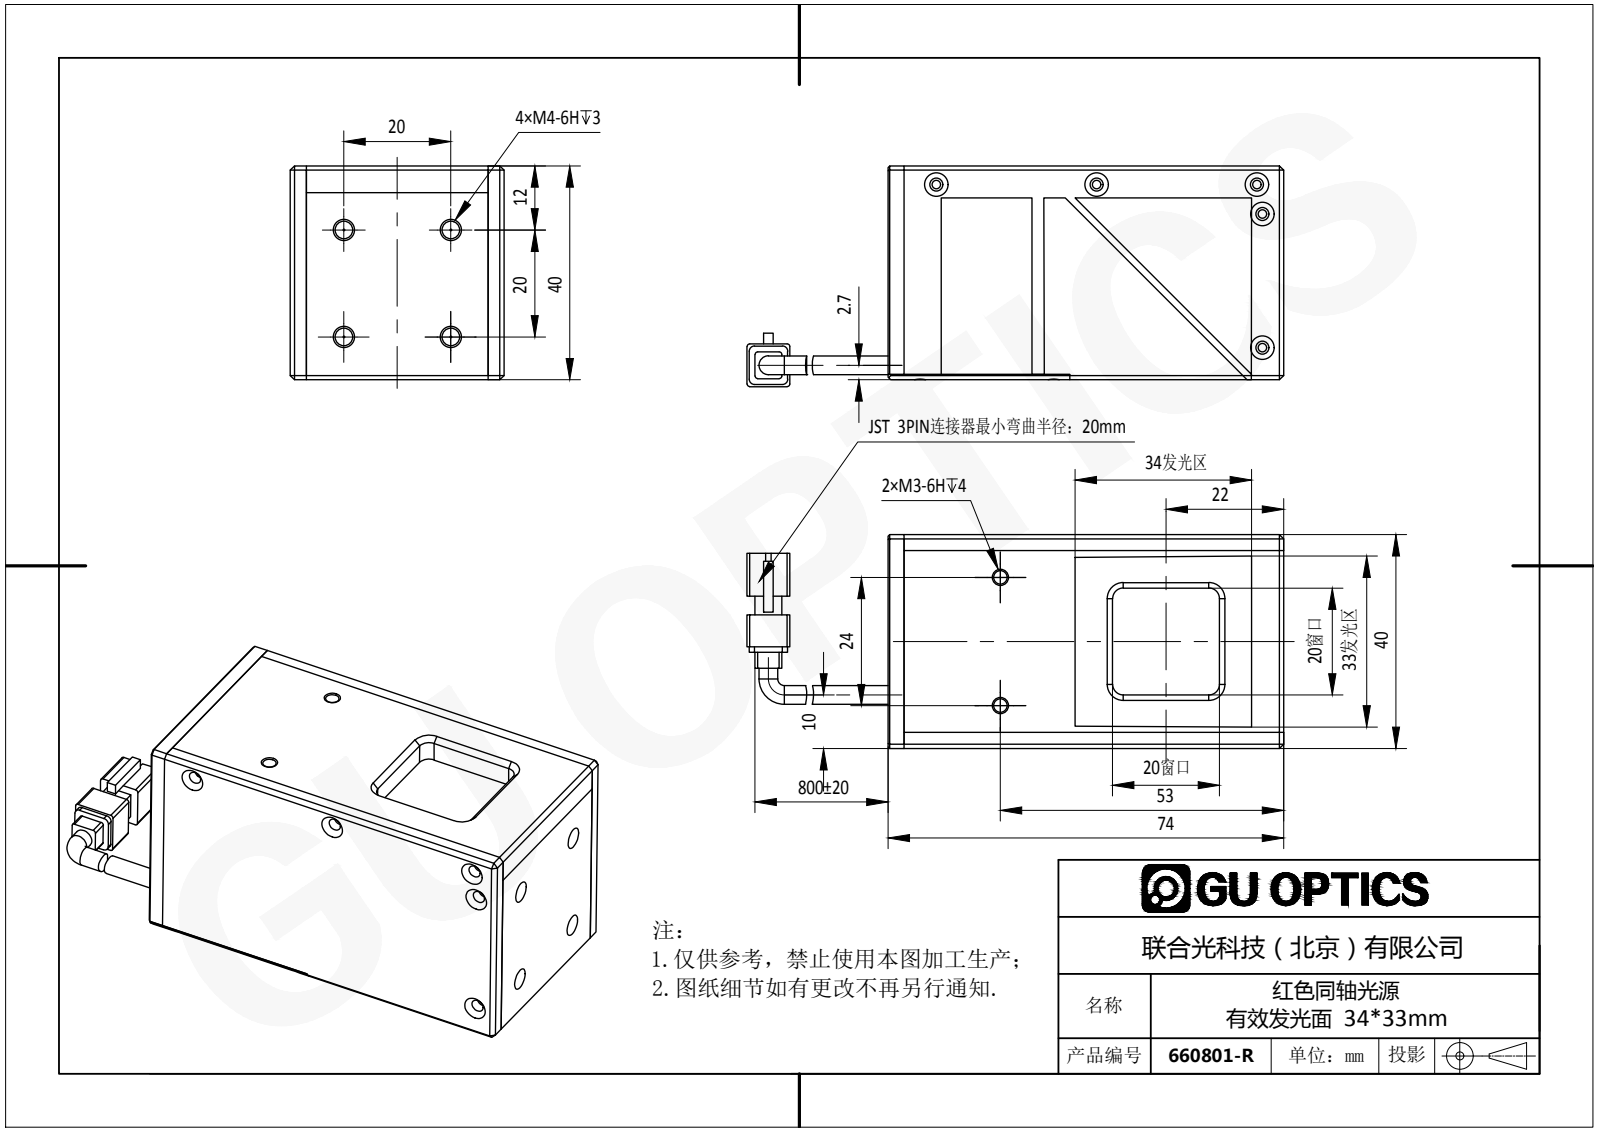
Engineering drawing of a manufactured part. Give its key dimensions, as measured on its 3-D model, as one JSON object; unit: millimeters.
{"step_written_by": "SolidWorks 2016 (AUTOMOTIVE_DESIGN)", "units": "millimeters", "bodies": {"solids": 10, "faces": 784, "planar": 471, "cylindrical": 153, "other": 160}, "overall_size": [100.39, 41.3, 40], "volume_mm3": 48647, "surface_area_mm2": 36045, "round_holes": [[1.6, 13], [2.4, 13], [4, 8], [2, 6], [3.3, 4], [2.5, 2]], "round_bosses_or_shafts": [[3.5, 2]], "partial_cylinders_radius": [[0.5, 8], [0.75, 6], [2, 5], [1, 4], [1.5, 4], [1.6, 3], [4, 1]], "face_to_face_distances": [1, 40, 3, 4, 36, 33, 34, 37, 6, 32], "hole_center_spacings": [30, 20, 25, 35, 7.5, 8.38, 11.41, 15.98]}
